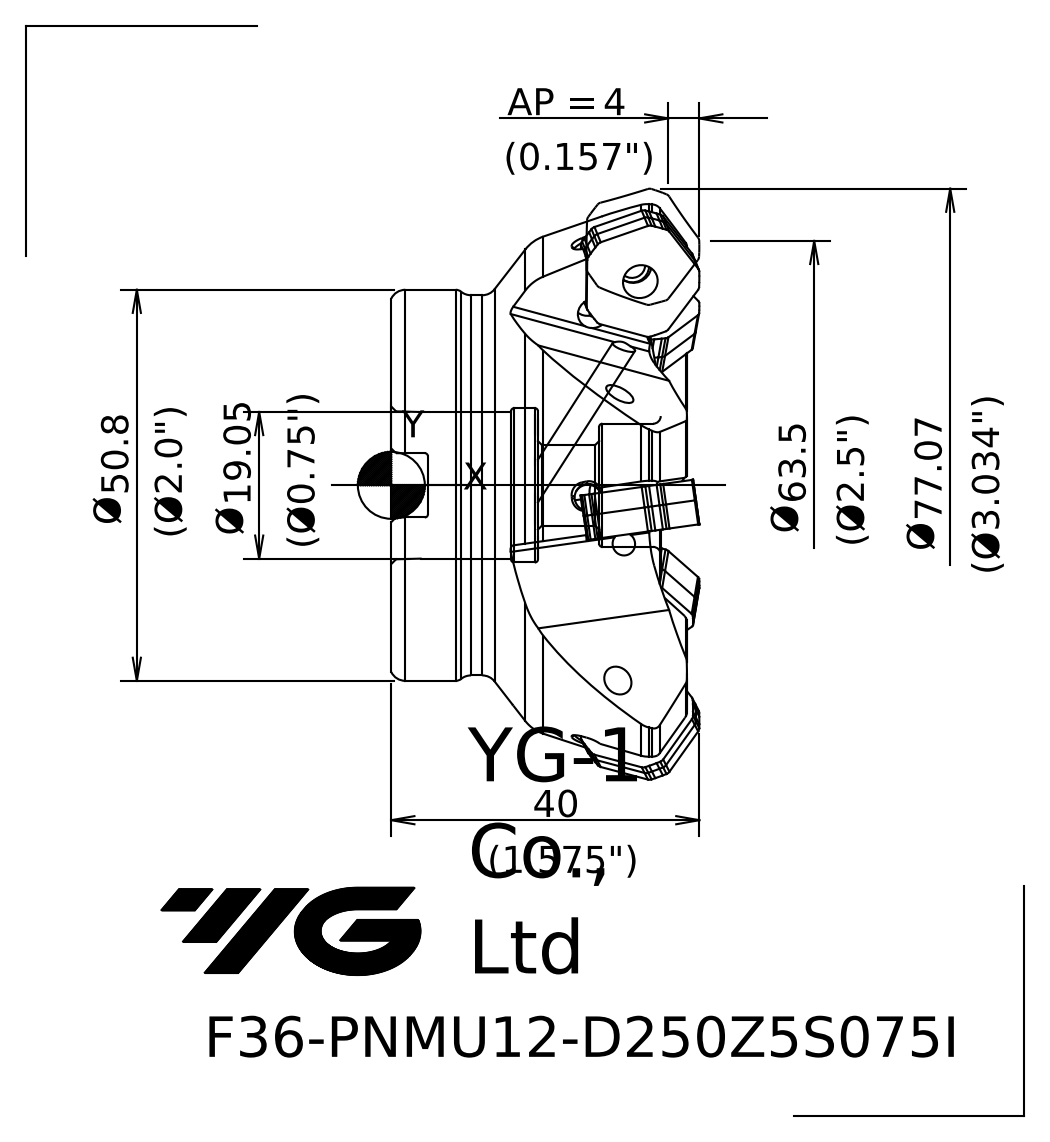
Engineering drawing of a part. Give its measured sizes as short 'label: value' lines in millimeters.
name: 120185C07CB1h7z5
written by: SIEMENS PLM Software NX 10.0 (AP203_CONFIGURATION_CONTROLLED_3D_DESIGN_OF_MECHANICAL_PARTS_AND_ASSEMBLIES_MIM_LF)
unit: mm
bodies: 1 solid, 69 faces (18 planar, 9 cylindrical, 42 other)
size: 77.07 × 77.07 × 40.01
volume: 106 143 mm³; area: 16 634 mm²
holes: 1× ⌀10.5, 1× ⌀19.05, 1× ⌀20.05
bosses: 1× ⌀50.8, 1× ⌀49.4
rounds: 2× R0.4
face distances: 34.15, 29.4, 4.75, 15.1, 14.3, 19.05, 0.85, 15.95, 30.25, 35
